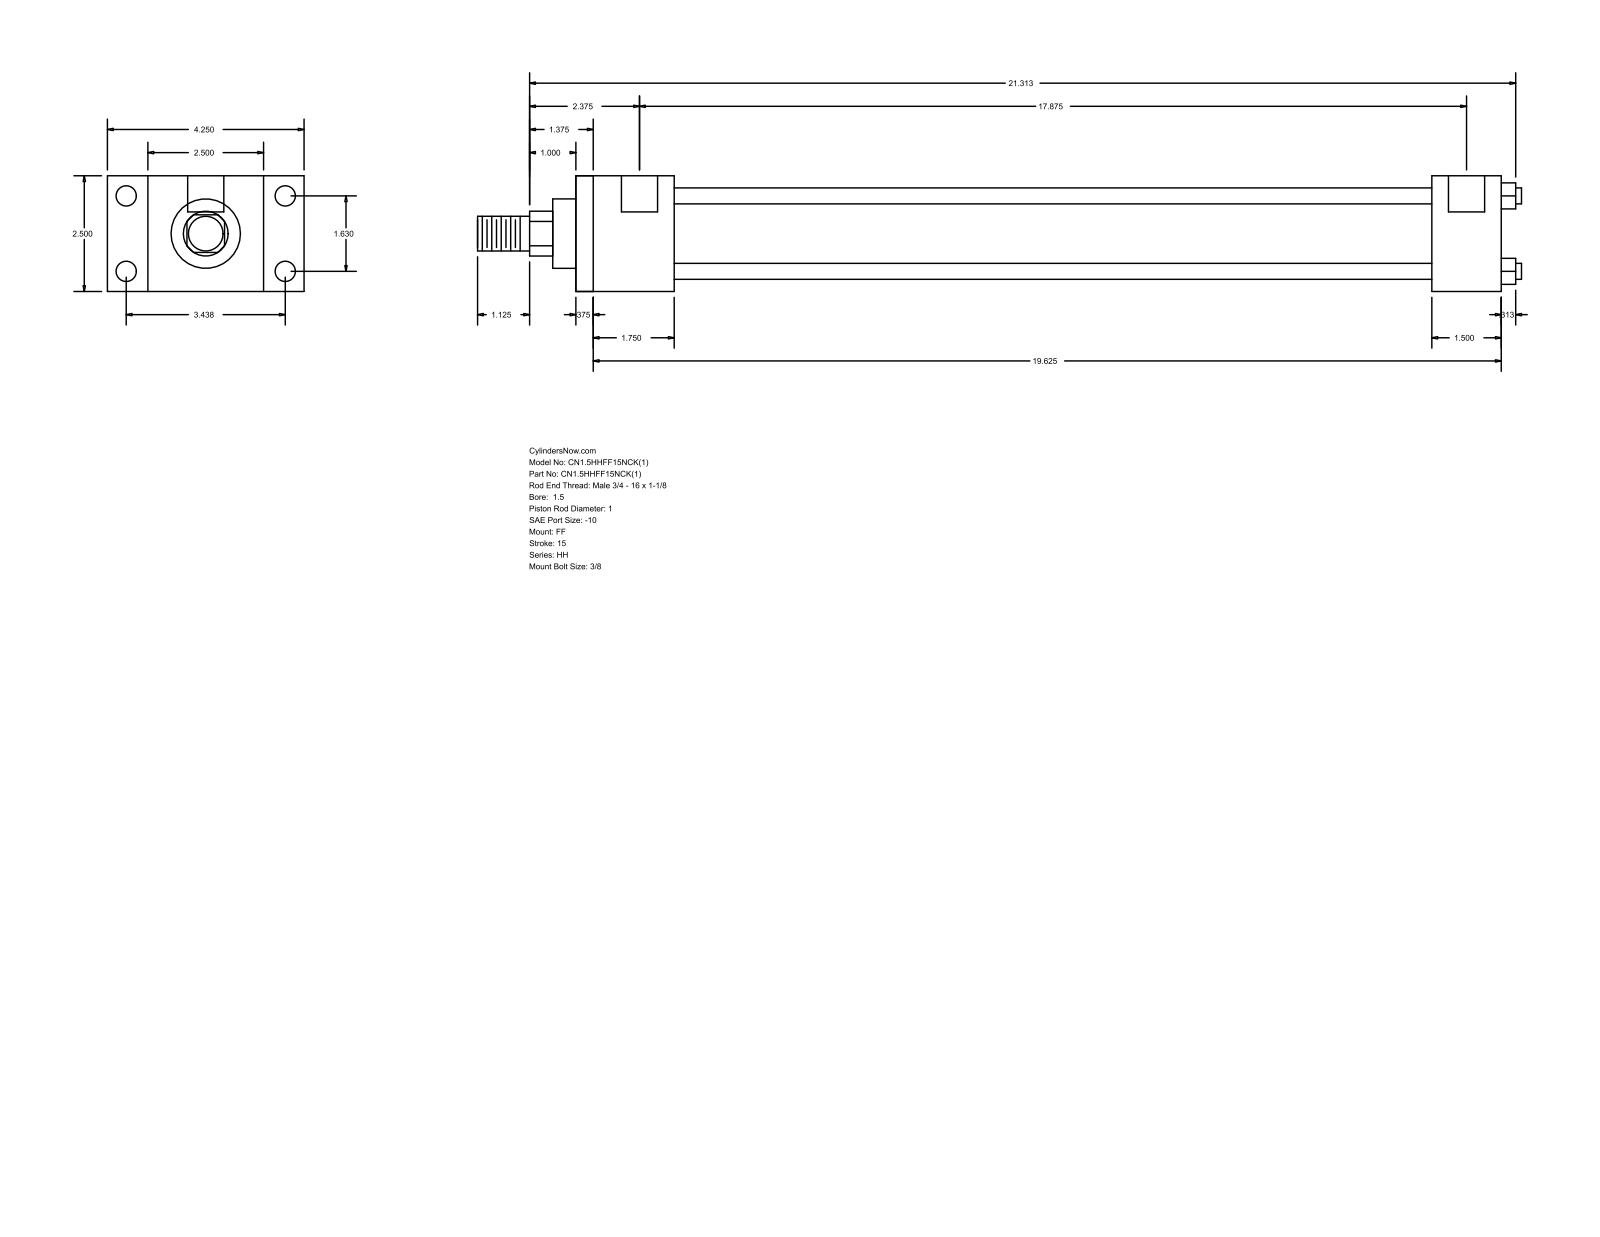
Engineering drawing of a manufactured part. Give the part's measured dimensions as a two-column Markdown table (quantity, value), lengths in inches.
| quantity | value |
| --- | --- |
| part name | HH_FF__0150_1 |
| STEP written by | GSSL Pune (CONFIG_CONTROL_DESIGN) |
| units | inches |
| bodies | 0 solids, 92 faces (64 planar, 28 cylindrical, 0 other) |
| overall size | 22.563 × 4.25 × 2.5 |
| round holes (diameter × count) | 0.219 × 4, 0.438 × 4, 0.781 × 2 |
| round bosses / shafts (diameter × count) | 0.345 × 4, 1.75 × 1, 1.5 × 1, 1 × 1, 0.75 × 1 |
| partial cylindrical surfaces (radius × count) | 0.484 × 1 |
| main face-to-face distances | 2.5, 20, 0.375, 19.625, 1.5, 2.125, 1.75, 17.875, 18.5, 18.125 |
| hole center spacings | 0.063, 1.63, 3.438, 3.805, 17.937, 18, 17.875 |
